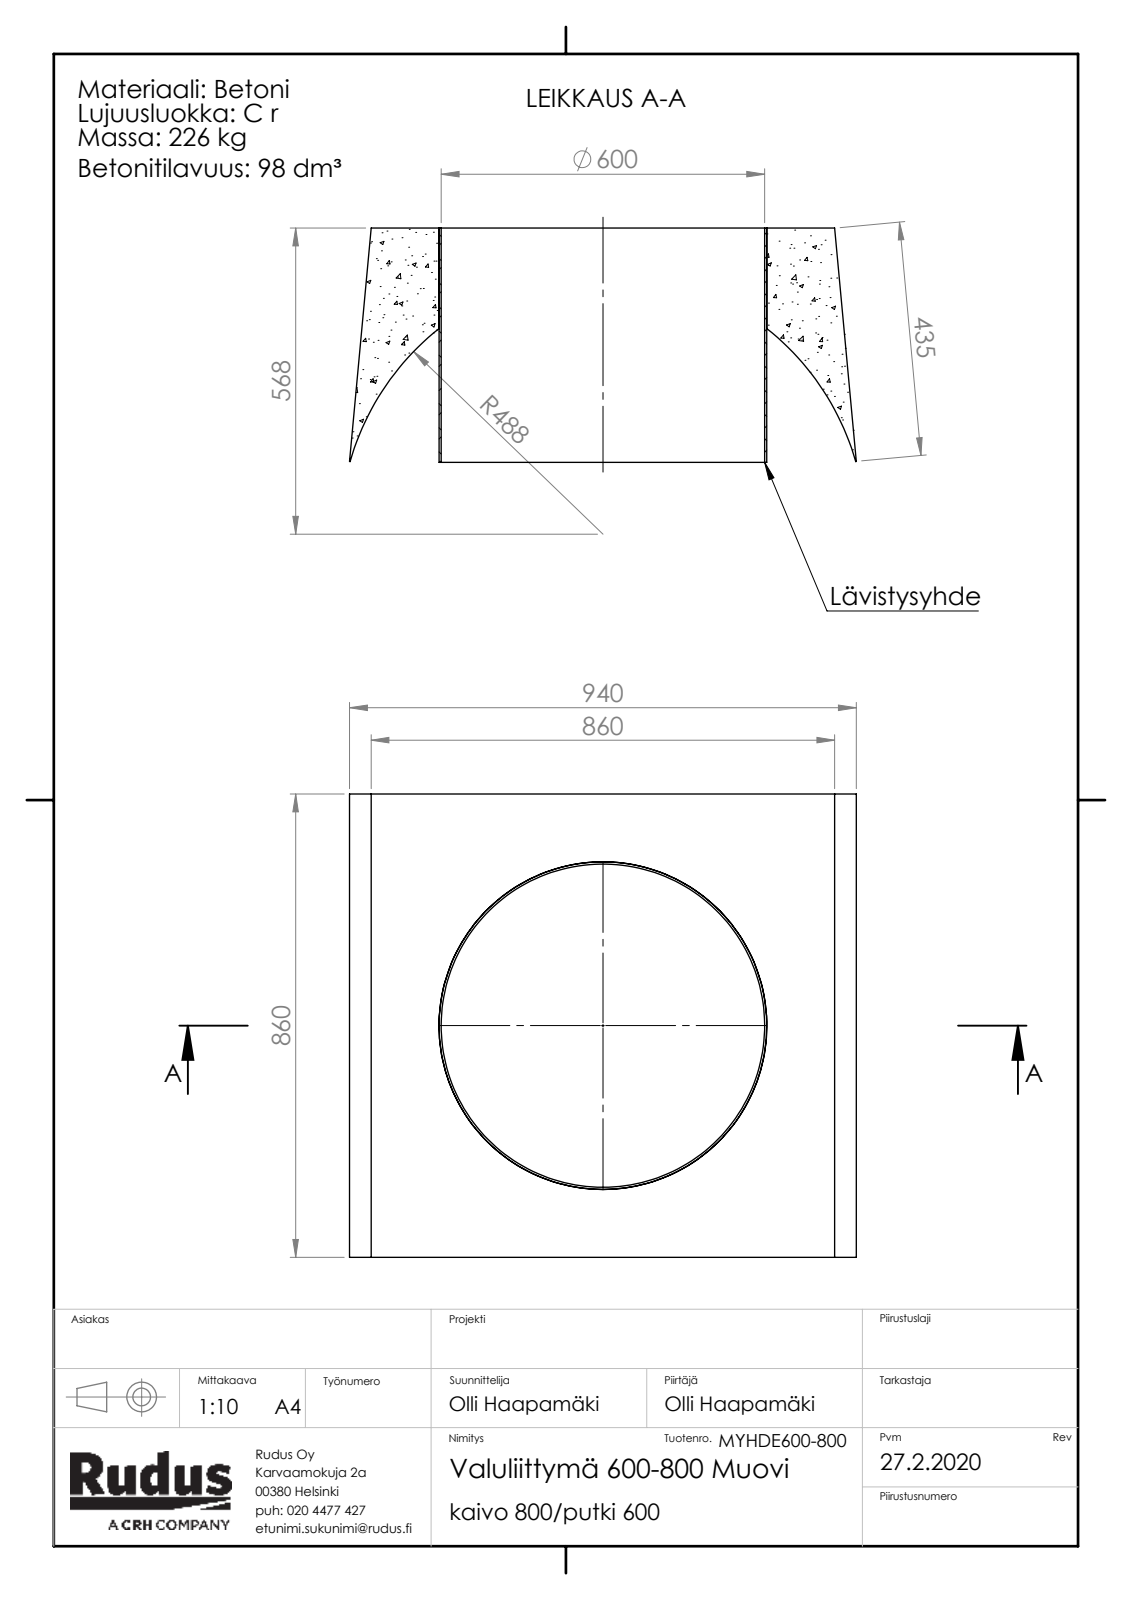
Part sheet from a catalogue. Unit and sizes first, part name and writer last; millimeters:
Units: millimetres
Overall size (bounding box): 940 × 860 × 435
Round holes (diameter × count): ⌀600 ×1, ⌀608 ×1
Partial cylindrical surfaces — rounded edges, fillets, slot ends (radius × count): R488 ×1
Main face-to-face distances: 860, 435
Volume: 98 180 000 mm³ · Surface area: 4 185 000 mm²
Bodies: 2 solids, 16 faces (9 planar, 7 cylindrical, 0 other)
Part name (STEP PRODUCT): Rudus MYHDE600-800 Valuliittymä 600-800 Muovi; muovi-lavistysyhde; kaivo-osa-valuliittyma-runko_muovi
STEP written by: SolidWorks 2019 (CONFIG_CONTROL_DESIGN)
